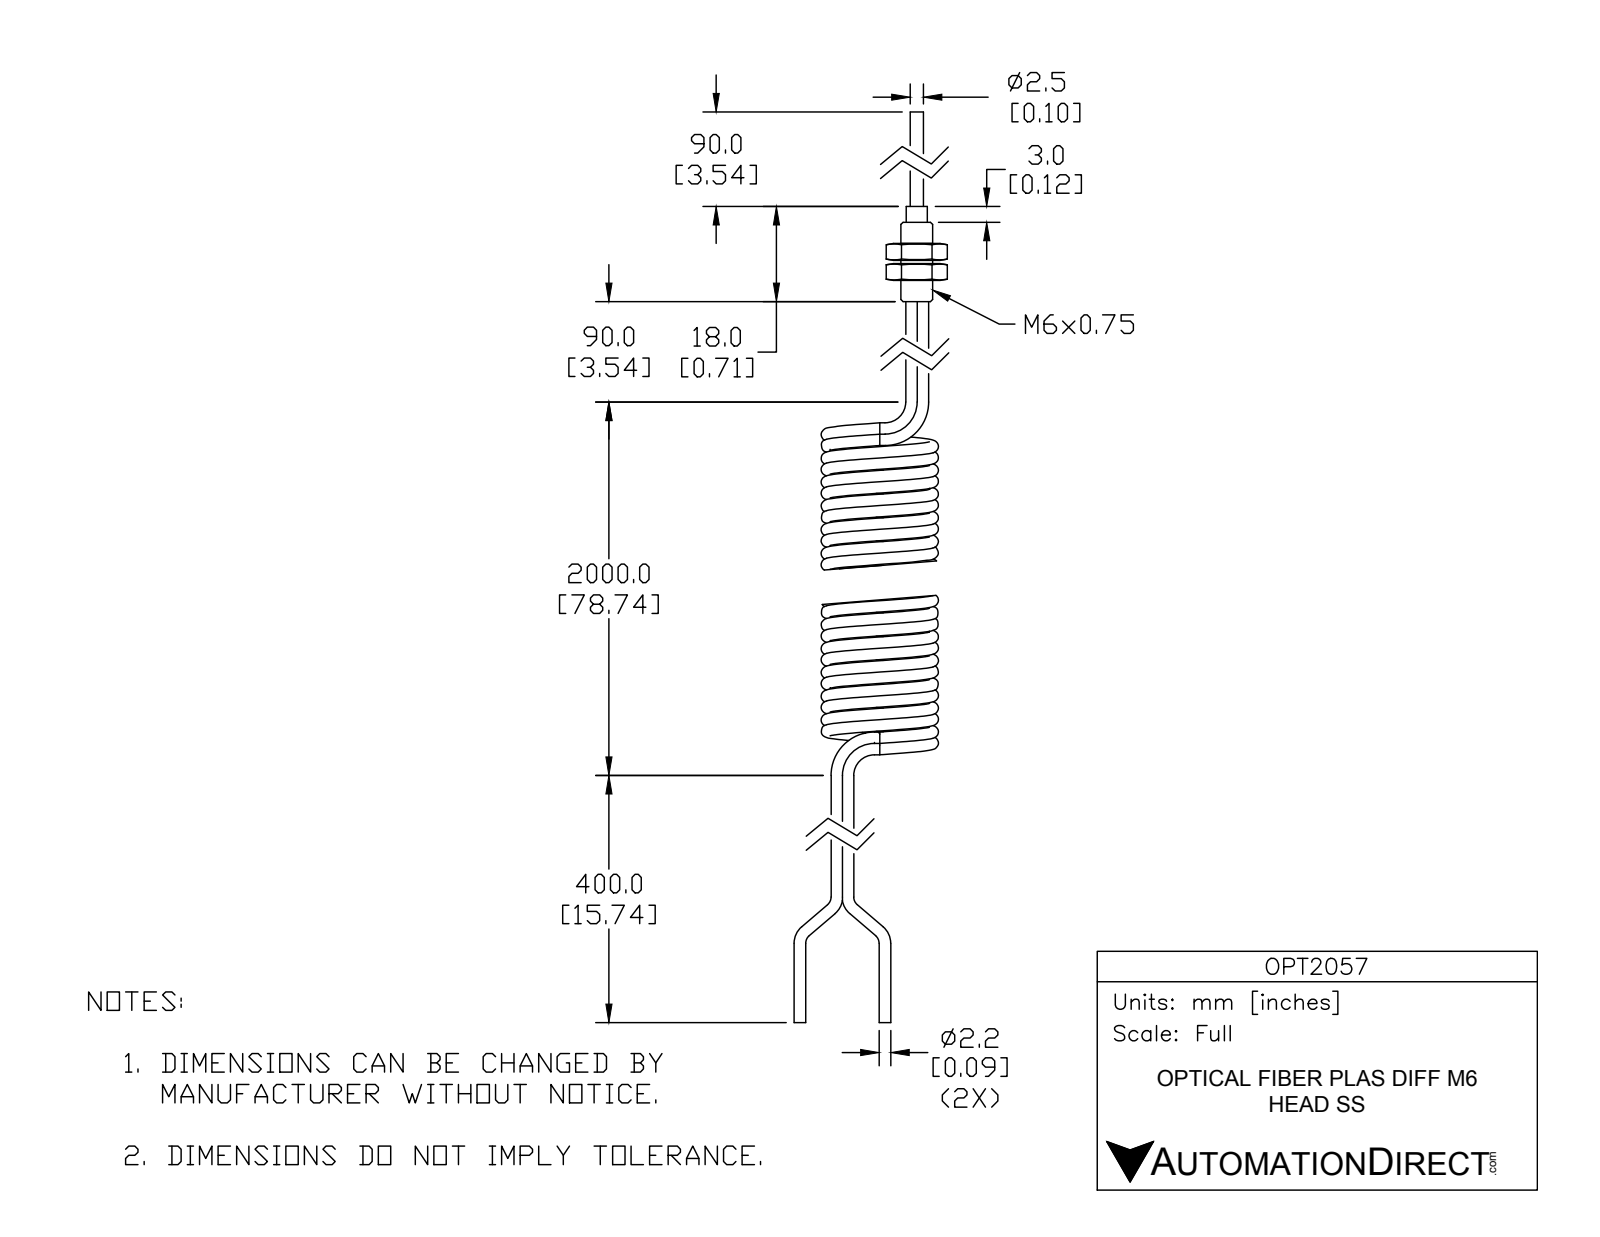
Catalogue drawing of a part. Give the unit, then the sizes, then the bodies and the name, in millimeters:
Units: millimetres
Overall size (bounding box): 182.4 × 29 × 26.1
Round bosses / shafts (diameter × count): ⌀2.2 ×12, ⌀6 ×1, ⌀4 ×1, ⌀2.5 ×1
Main face-to-face distances: 10, 6.5, 3.2, 3.8, 7, 0.6, 4, 7.2, 7.8, 11
Volume: 7 130 mm³ · Surface area: 11 090 mm²
Bodies: 6 solids, 124 faces (41 planar, 51 cylindrical, 32 other)
Part name (STEP PRODUCT): OPT2057
STEP written by: SolidWorks 2014 (AUTOMOTIVE_DESIGN)
